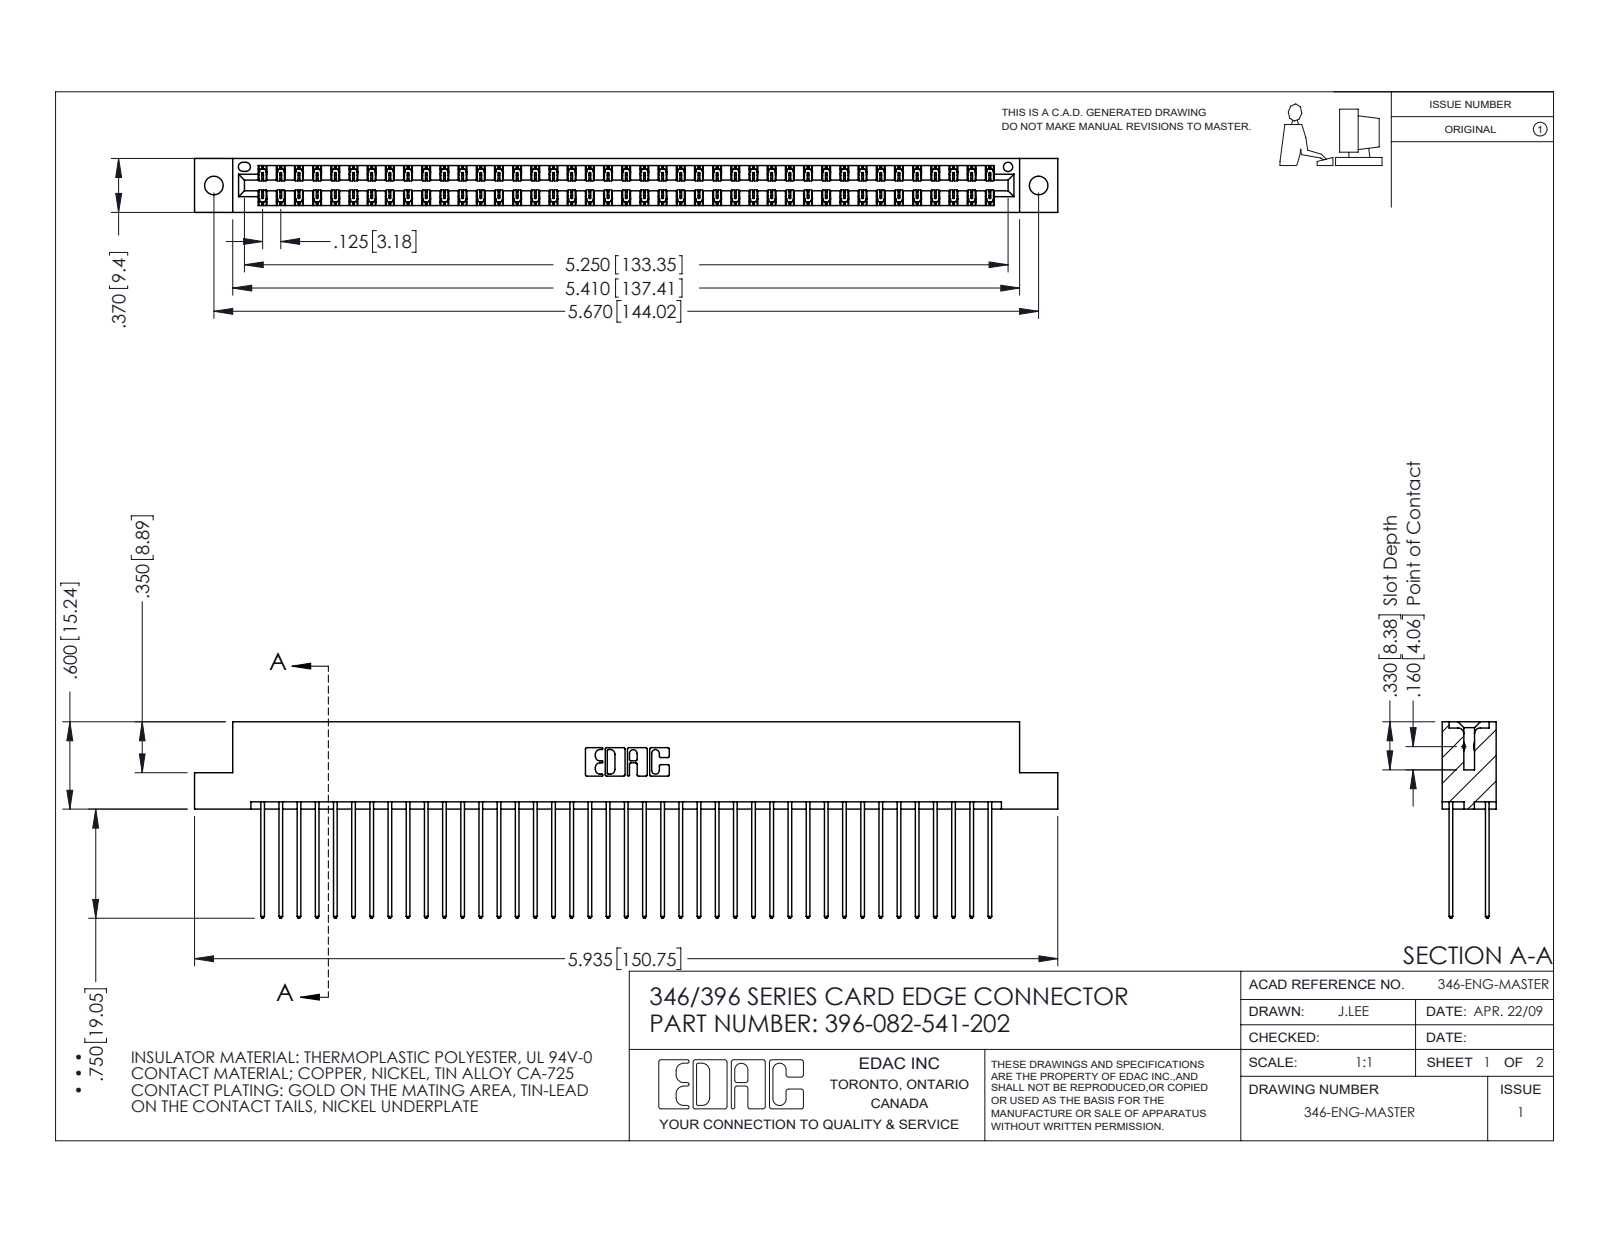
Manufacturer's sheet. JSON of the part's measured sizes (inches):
{"part_name": "345-292-001_345-293-141; 346 Part_Flush Mounting Lugs - 0.128 Dia; 396-082-541-202", "step_written_by": "SolidWorks 2016 (CONFIG_CONTROL_DESIGN)", "units": "inches", "bodies": {"solids": 83, "faces": 4386, "planar": 2946, "cylindrical": 1440, "other": 0}, "overall_size": [5.935, 1.35, 0.37], "volume_in3": 0.923, "surface_area_in2": 35.28, "round_holes": [[0.128, 2], [0.064, 1]], "partial_cylinders_radius": [[0.006, 123], [0.01, 82], [0.01, 22], [0.007, 6], [0.031, 6], [0.026, 3], [0.014, 2], [0.022, 2]], "face_to_face_distances": [0.048, 0.322, 0.25, 0.072, 0.298, 0.025, 0.37, 0.275, 0.225, 0.148], "hole_center_spacings": [0.246, 5.461, 5.67]}
